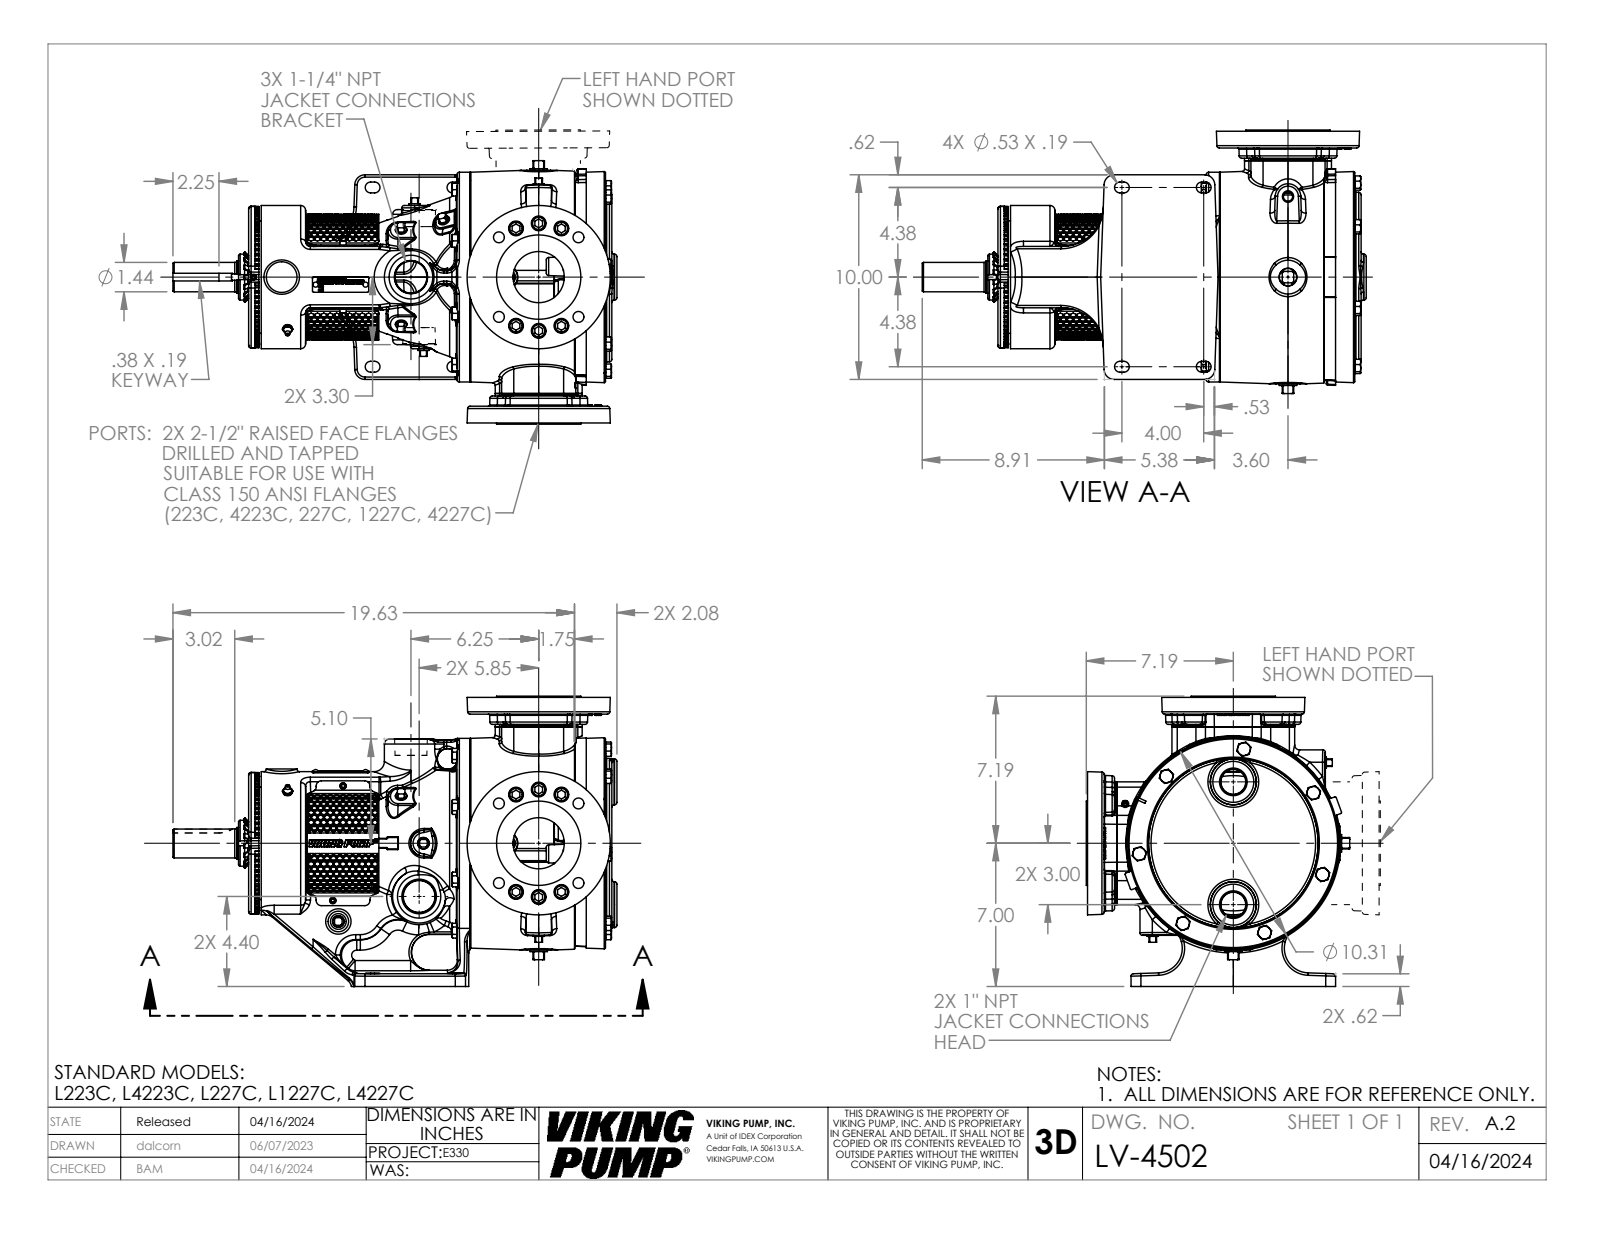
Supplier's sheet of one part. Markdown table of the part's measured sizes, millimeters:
| quantity | value |
| --- | --- |
| part name | LV-4502 |
| STEP written by | SolidWorks 2022 (AUTOMOTIVE_DESIGN) |
| units | millimeters |
| bodies | 1 solid, 7504 faces (2397 planar, 919 cylindrical, 4188 other) |
| overall size | 551.41 × 360.36 × 329.77 |
| volume | 17 920 000 mm³ |
| surface area | 866 169 mm² |
| round holes (diameter × count) | 18.26 × 12, 13.49 × 8, 27.79 × 8, 5.05 × 6, 6.35 × 6, 4.04 × 3, 6.76 × 2, 7.94 × 2, 63.5 × 2, 5.41 × 1, 11.51 × 1, 40.07 × 1 |
| round bosses / shafts (diameter × count) | 16.76 × 12, 15.88 × 11, 15.87 × 4, 11.11 × 3, 7.92 × 3, 104.65 × 2, 260.35 × 1, 177.8 × 1 |
| partial cylindrical surfaces (radius × count) | 1.61 × 109, 1.75 × 74, 3.05 × 68, 0.25 × 34, 0.24 × 28, 12.7 × 26, 0.76 × 18, 6.1 × 16 |
| main face-to-face distances | 7.88, 358.84, 57.15, 12.7, 69.85, 373.35, 381.23, 20.83, 22.35, 1.52 |
| hole center spacings | 76.2, 66.68, 69.85, 34.93, 23.91, 28.86, 52.33, 55.37 |
